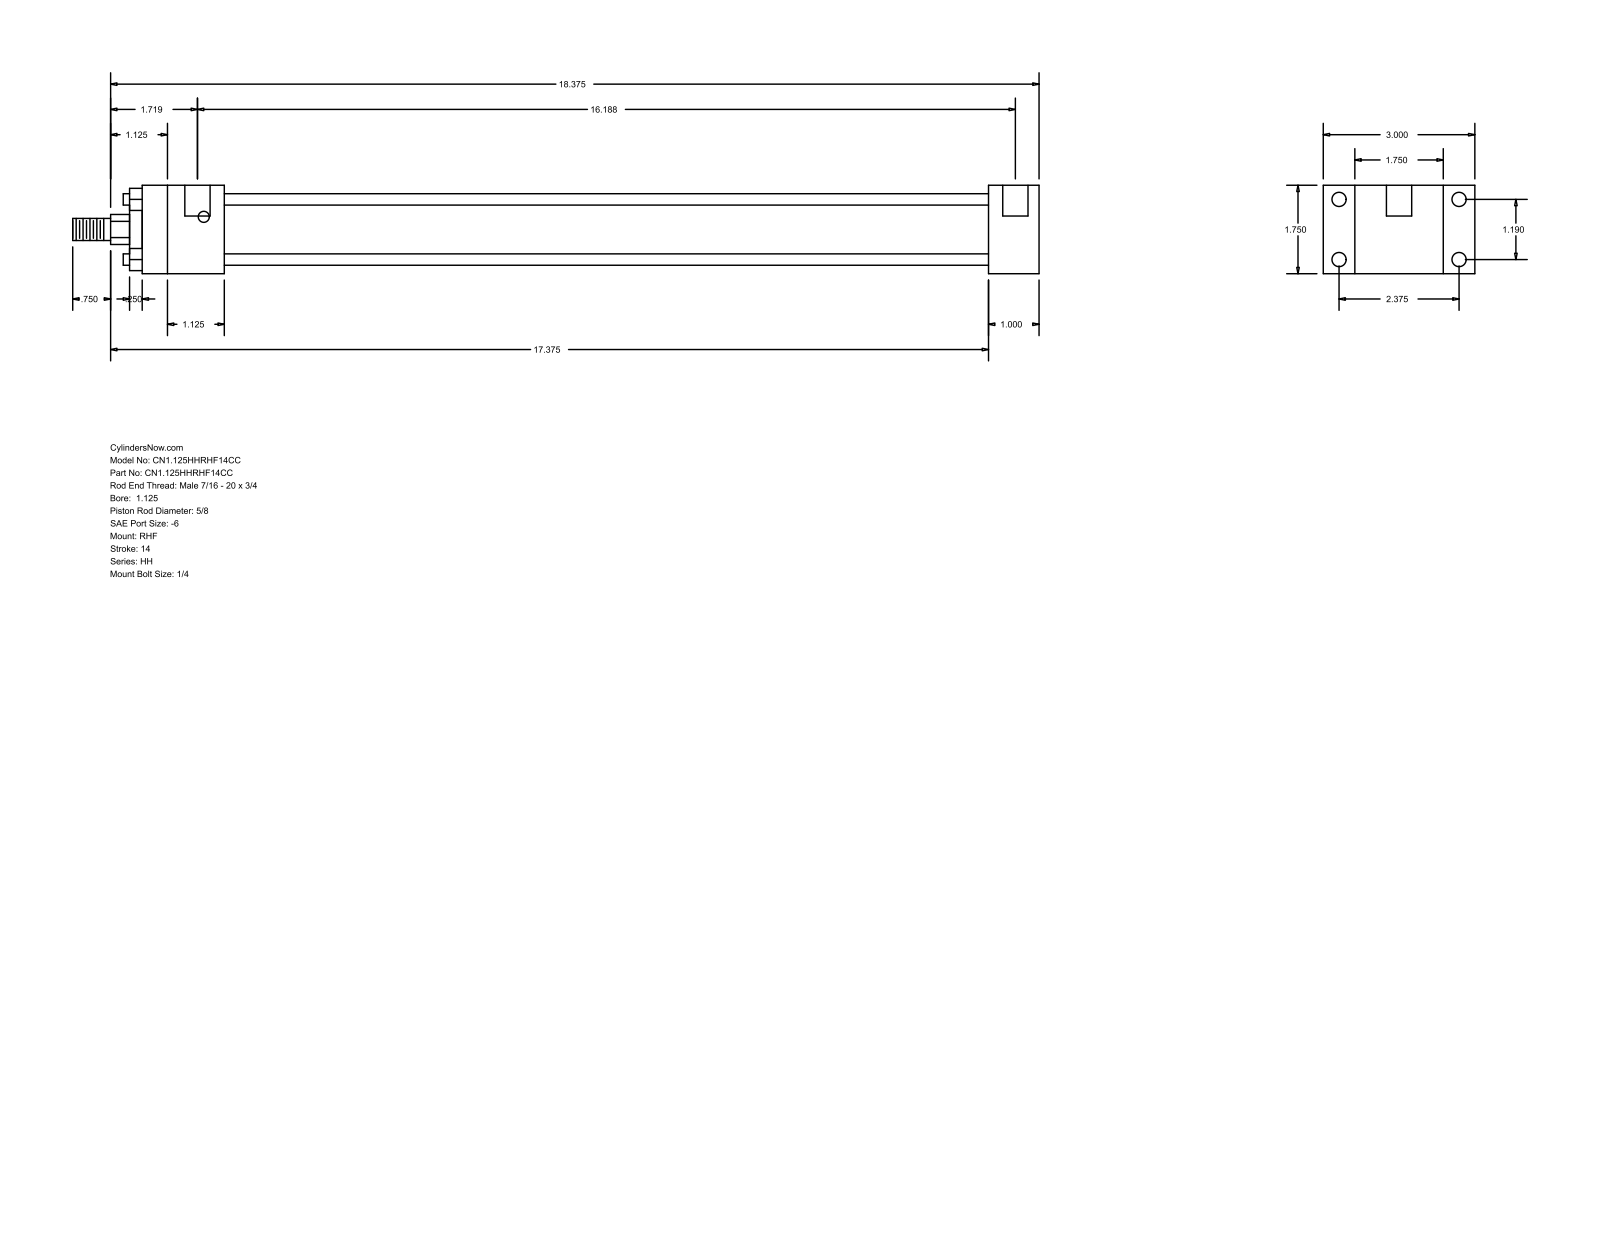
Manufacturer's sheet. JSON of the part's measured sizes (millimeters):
{"part_name": "HH_RHF__0112_0.625", "step_written_by": "GSSL Pune (CONFIG_CONTROL_DESIGN)", "units": "millimeters", "bodies": {"solids": 0, "faces": 88, "planar": 60, "cylindrical": 28, "other": 0}, "overall_size": [485.77, 76.2, 44.45], "round_holes": [[5.56, 4], [7.14, 4], [12.7, 2]], "round_bosses_or_shafts": [[5.71, 4], [34.92, 1], [28.57, 1], [15.88, 1], [11.11, 1]], "partial_cylinders_radius": [[7.54, 1]], "face_to_face_distances": [44.46, 15.87, 60.33, 25.41, 76.2, 384.17, 409.58, 41.27, 425.44, 450.85], "hole_center_spacings": [30.22, 60.32, 67.47, 407.99, 3.17, 411.16]}
